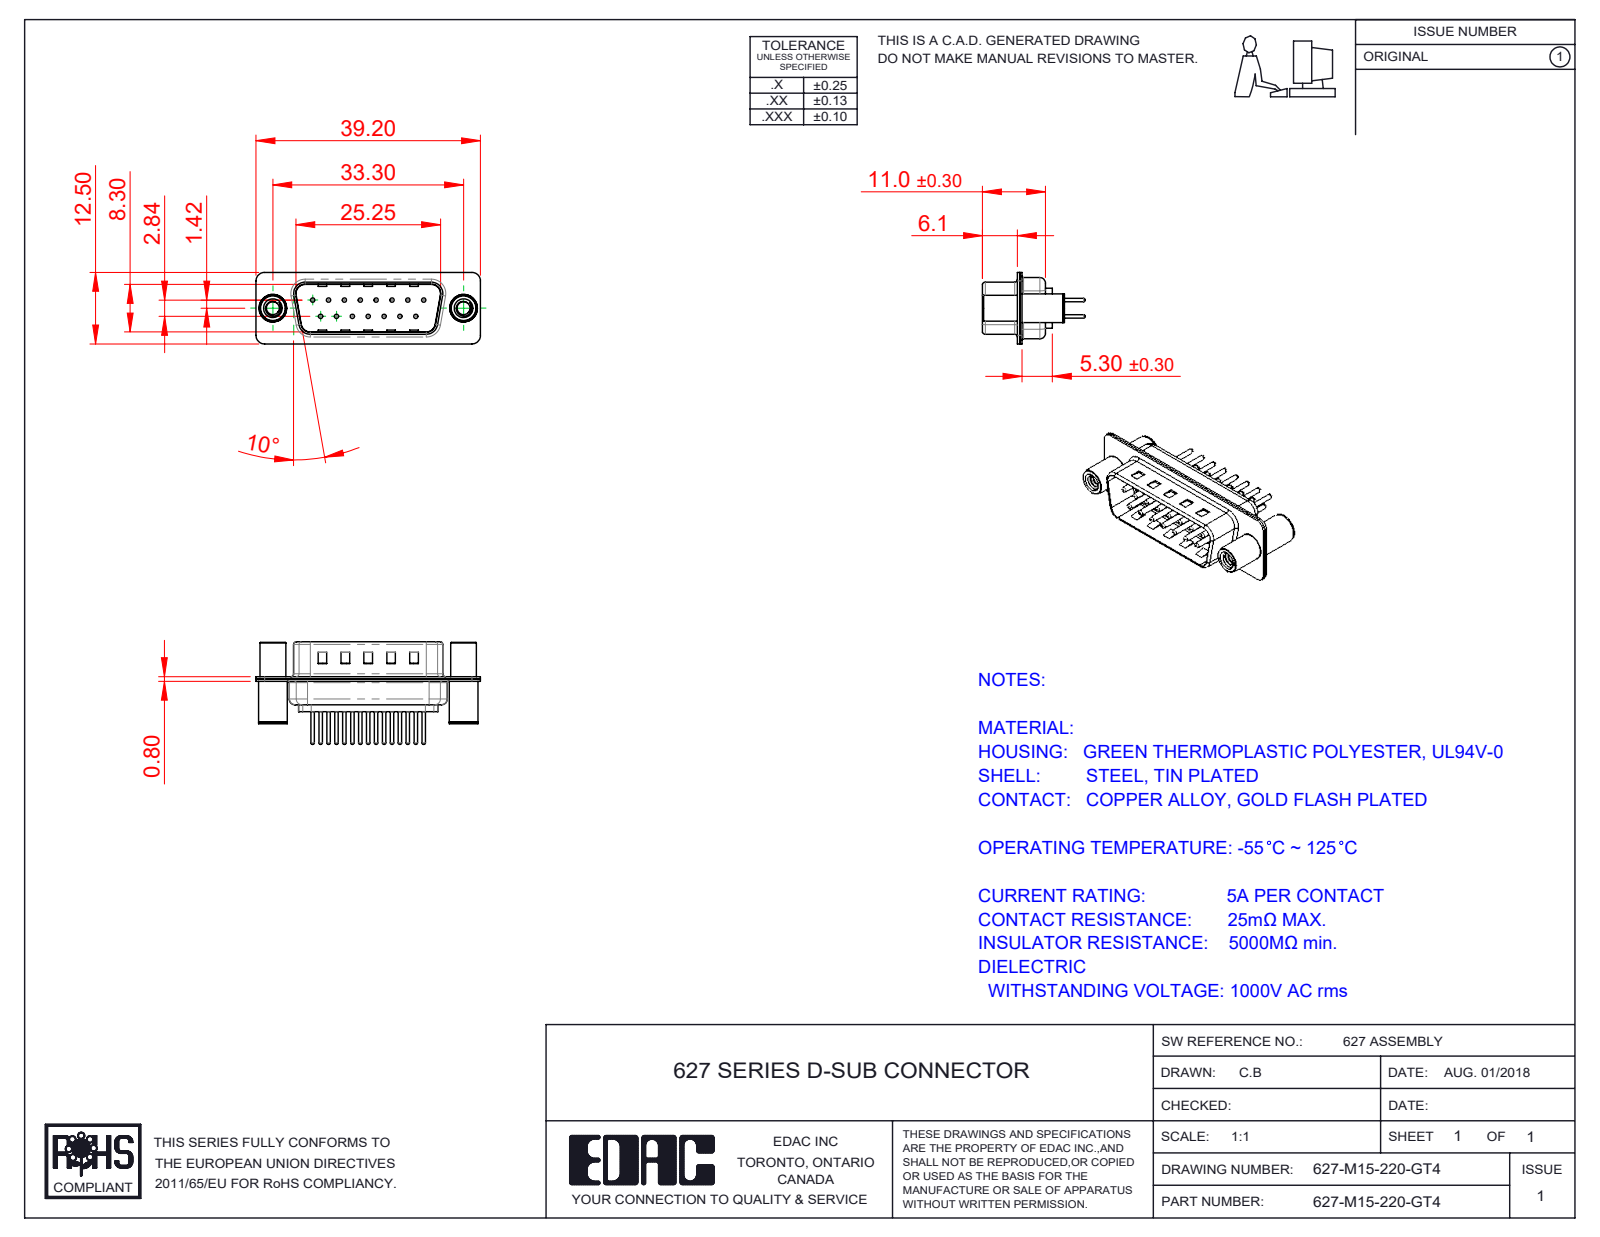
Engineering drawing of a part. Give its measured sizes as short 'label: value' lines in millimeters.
name: 627M Shell Front_15 Contacts; 627M Contact Row 2_20; 627M Shell Rear_15 Contacts; 627M 4-40 Threaded Standoff and Board Spacer (+3 more)
written by: SolidWorks 2020 (CONFIG_CONTROL_DESIGN)
unit: mm
bodies: 20 solids, 981 faces (250 planar, 395 cylindrical, 336 other)
size: 39.2 × 17.9 × 12.5
volume: 2 130 mm³; area: 5 337 mm²
holes: 15× ⌀0.75, 15× ⌀1.6, 15× ⌀2, 2× ⌀2.26, 2× ⌀3.26, 2× ⌀4, 2× ⌀4.8
bosses: 15× ⌀1.5, 15× ⌀0.6, 2× ⌀5, 2× ⌀4.9, 2× ⌀4.5
rounds: 16× R1.5, 12× R2, 8× R0.5, 8× R1.6, 4× R0.25, 4× R0.6, 4× R0.65, 4× R0.9
face distances: 0.4, 0.8, 9.5, 9.1, 8.7, 9.9, 1.2, 5.3, 6.1, 5.7
hole spacings: 3.16, 2.77, 5.54, 8.31, 11.08, 5.03, 5.04, 7.48
